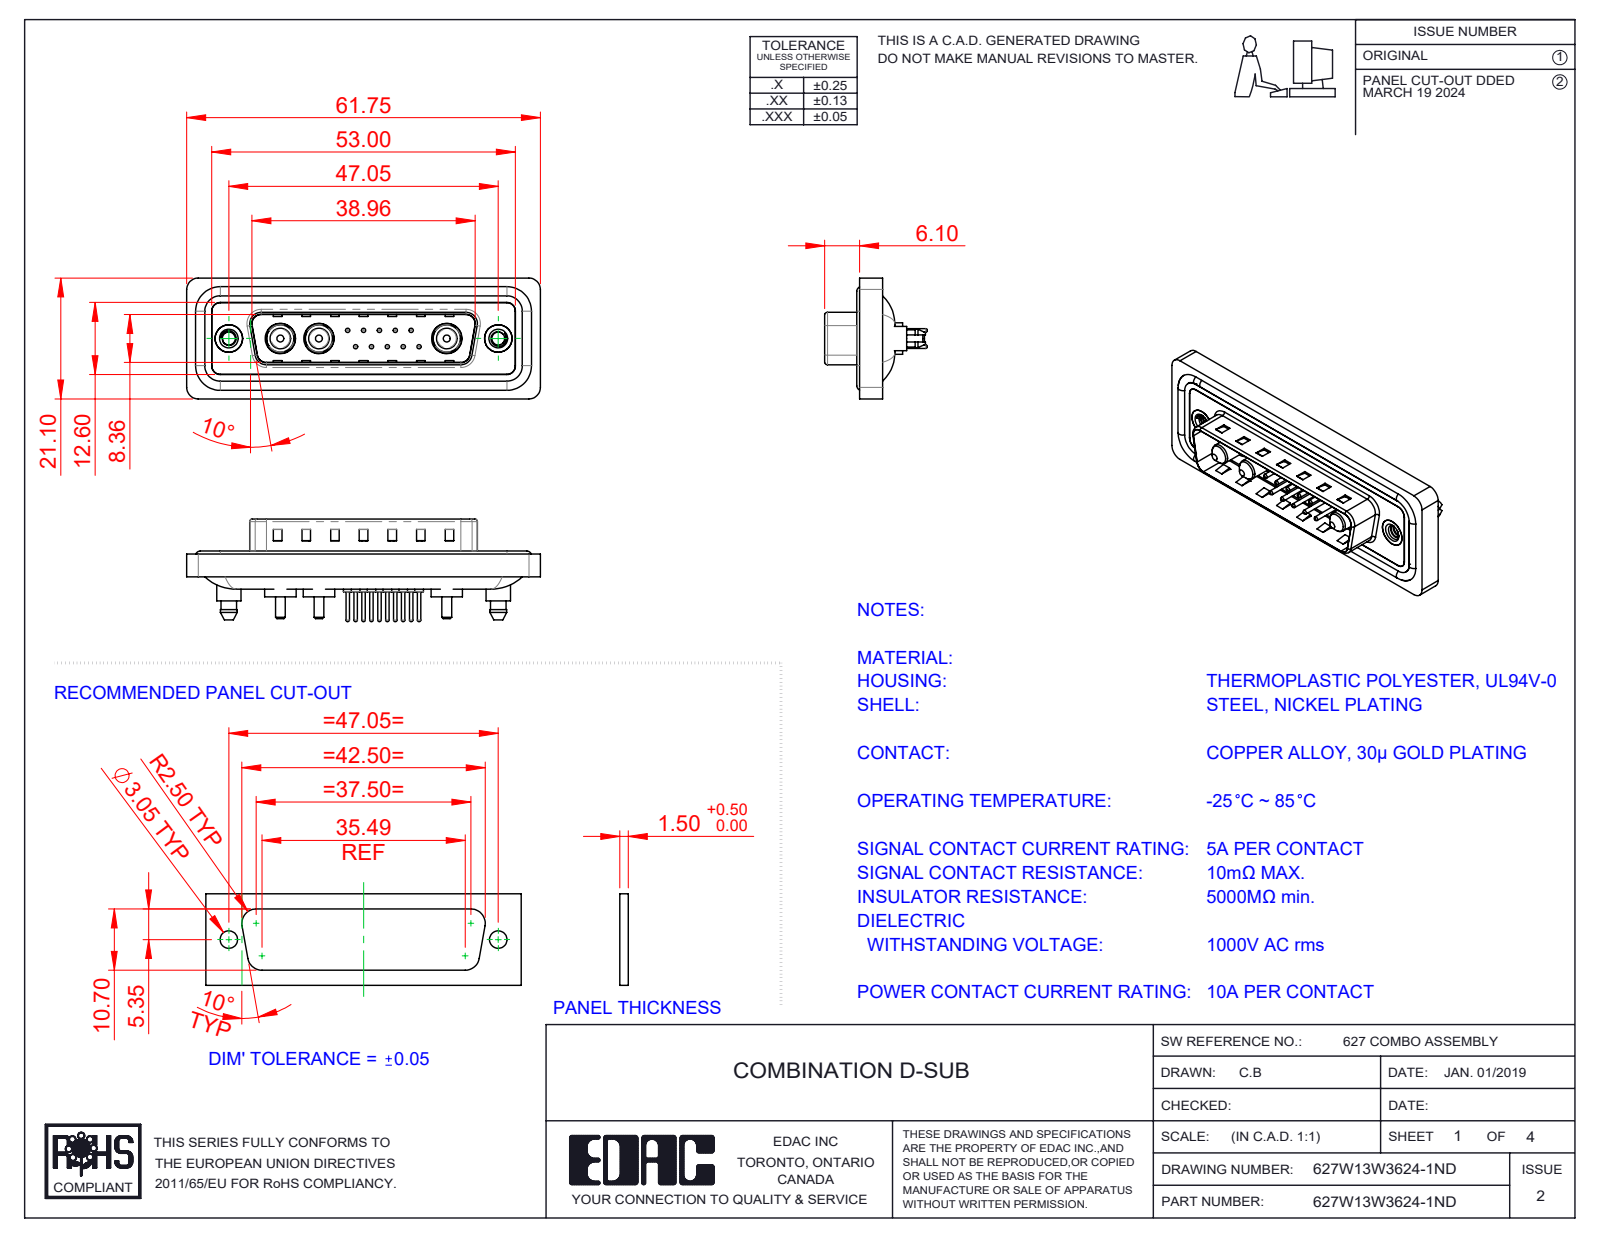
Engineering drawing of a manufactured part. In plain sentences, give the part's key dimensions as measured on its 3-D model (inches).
The part is named "627Combo Shell Front_25 Contacts; 627Combo Threaded Boardlock_5; Power Pin_10A S; 627Combo Housing_13W3 (+6 more)". Its 3-D file was written by "SolidWorks 2023 (CONFIG_CONTROL_DESIGN)". It is 23 solids with 1028 faces: 325 planar, 425 cylindrical and 278 other. Overall it measures 2.431 by 0.831 by 0.705 inches. Its volume is 0.453 cubic inches and its surface area 18.87 square inches. Round holes: 10 of diameter 0.03, 10 of diameter 0.063, 10 of diameter 0.079, 3 of diameter 0.191, 3 of diameter 0.209, 2 of diameter 0.089, 2 of diameter 0.157, 2 of diameter 0.189, 2 of diameter 0.197. Round bosses or shafts: 10 of diameter 0.059, 10 of diameter 0.024, 4 of diameter 0.063, 3 of diameter 0.217, 3 of diameter 0.205, 3 of diameter 0.187, 3 of diameter 0.148, 3 of diameter 0.142. Partial cylindrical surfaces (rounded edges, fillets, slot ends): 24 of radius 0.059, 18 of radius 0.079, 10 of radius 0.063, 8 of radius 0.02, 4 of radius 0.01, 4 of radius 0.024, 4 of radius 0.026, 4 of radius 0.035. The main face-to-face distances are 0.016, 0.059, 0.043, 0.063, 0.02, 0.122, 0.114, 0.032, 0.377, 0.161. The hole center spacings are 0.124, 0.109, 0.198, 0.218, 0.295, 0.198, 0.327, 0.398.
